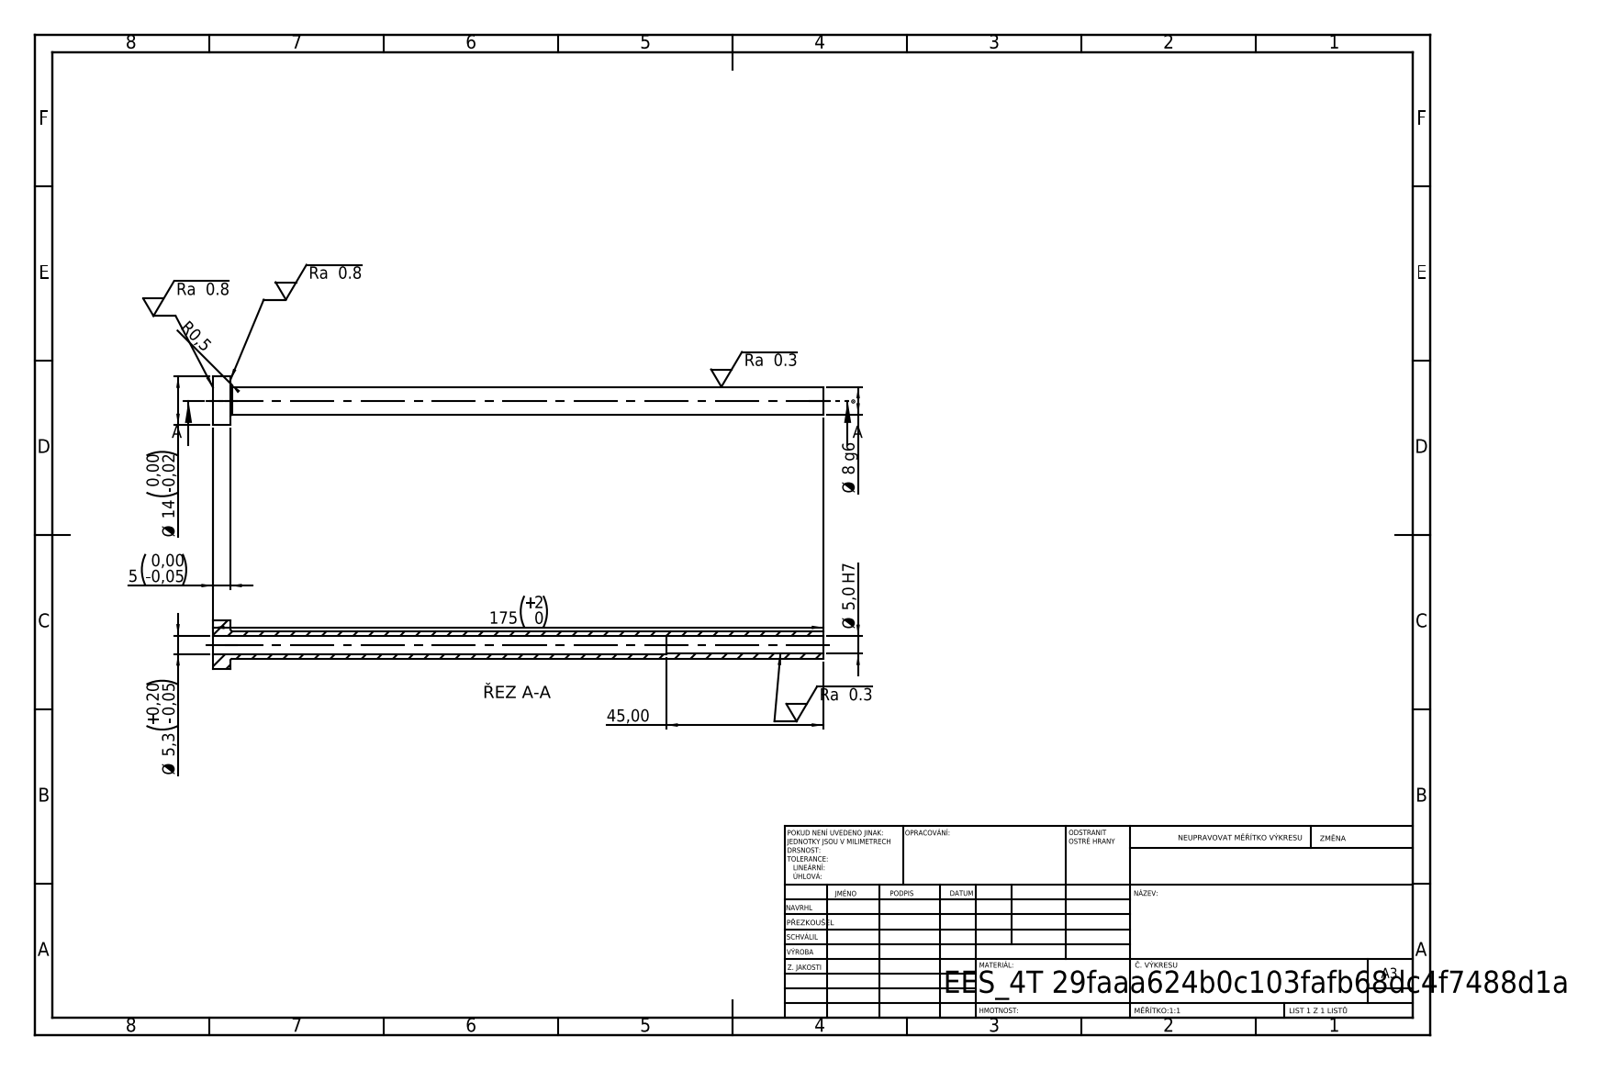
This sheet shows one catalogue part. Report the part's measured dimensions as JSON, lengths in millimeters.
{"step_written_by": "SolidWorks 2019 (CONFIG_CONTROL_DESIGN)", "units": "millimeters", "bodies": {"solids": 1, "faces": 14, "planar": 4, "cylindrical": 8, "other": 2}, "overall_size": [175, 14, 14], "volume_mm3": 5565, "surface_area_mm2": 7627, "round_holes": [[5, 1], [5.3, 1]], "round_bosses_or_shafts": [[14, 1], [8, 1]], "face_to_face_distances": [5, 175, 170, 130, 125, 45]}
